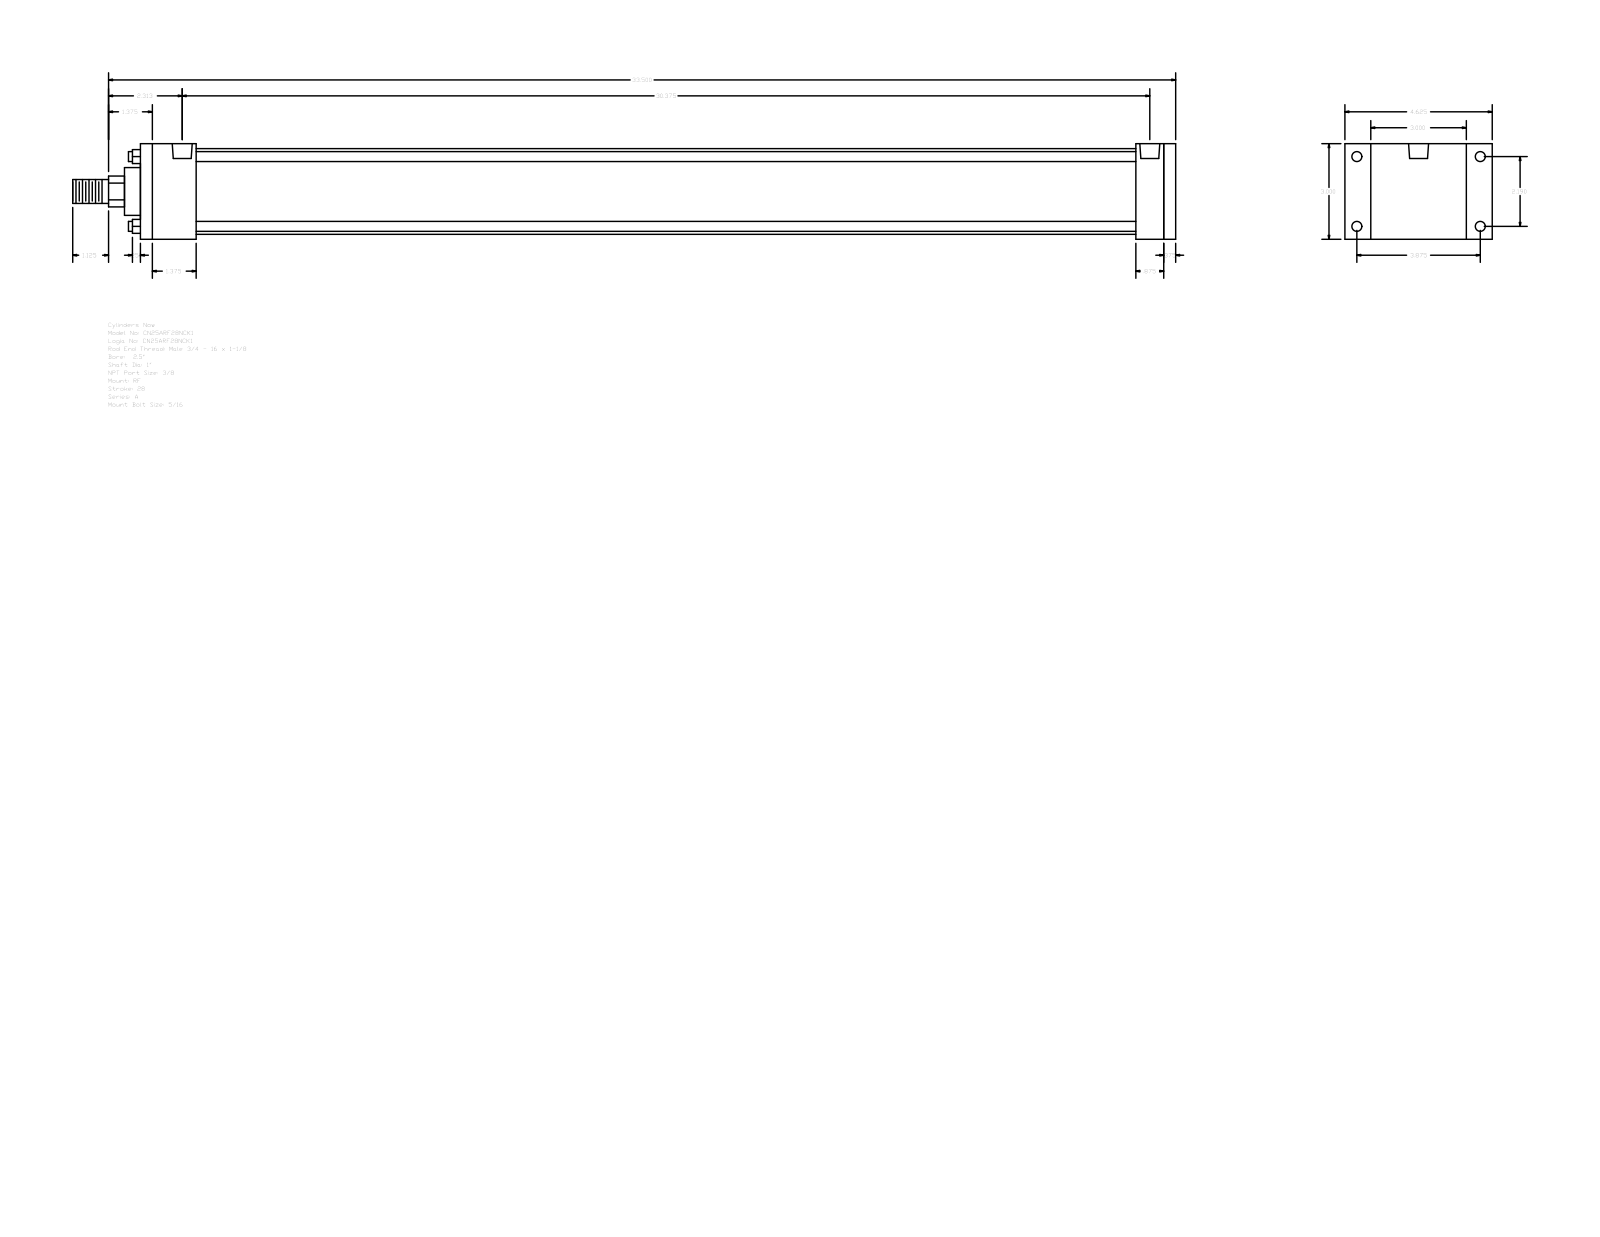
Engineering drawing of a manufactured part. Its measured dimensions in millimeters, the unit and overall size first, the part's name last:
Units: millimetres
Overall size (bounding box): 879.48 × 117.47 × 76.2
Round holes (diameter × count): ⌀5.56 ×4, ⌀7.94 ×4, ⌀15.93 ×2
Round bosses / shafts (diameter × count): ⌀7.94 ×4, ⌀68.33 ×1, ⌀38.1 ×1, ⌀25.4 ×1, ⌀19.05 ×1
Partial cylindrical surfaces — rounded edges, fillets, slot ends (radius × count): R12.29 ×1
Main face-to-face distances: 76.2, 825.5, 9.52, 815.98, 44.45, 793.75, 749.3, 771.53, 781.05, 22.23
Hole centre spacings: 2.38, 55.62, 98.42, 113.05, 773.9, 776.28, 771.52
Bodies: 0 solids, 92 faces (64 planar, 28 cylindrical, 0 other)
Part name (STEP PRODUCT): A_RF__0250_1
STEP written by: GSSL Pune (CONFIG_CONTROL_DESIGN)
